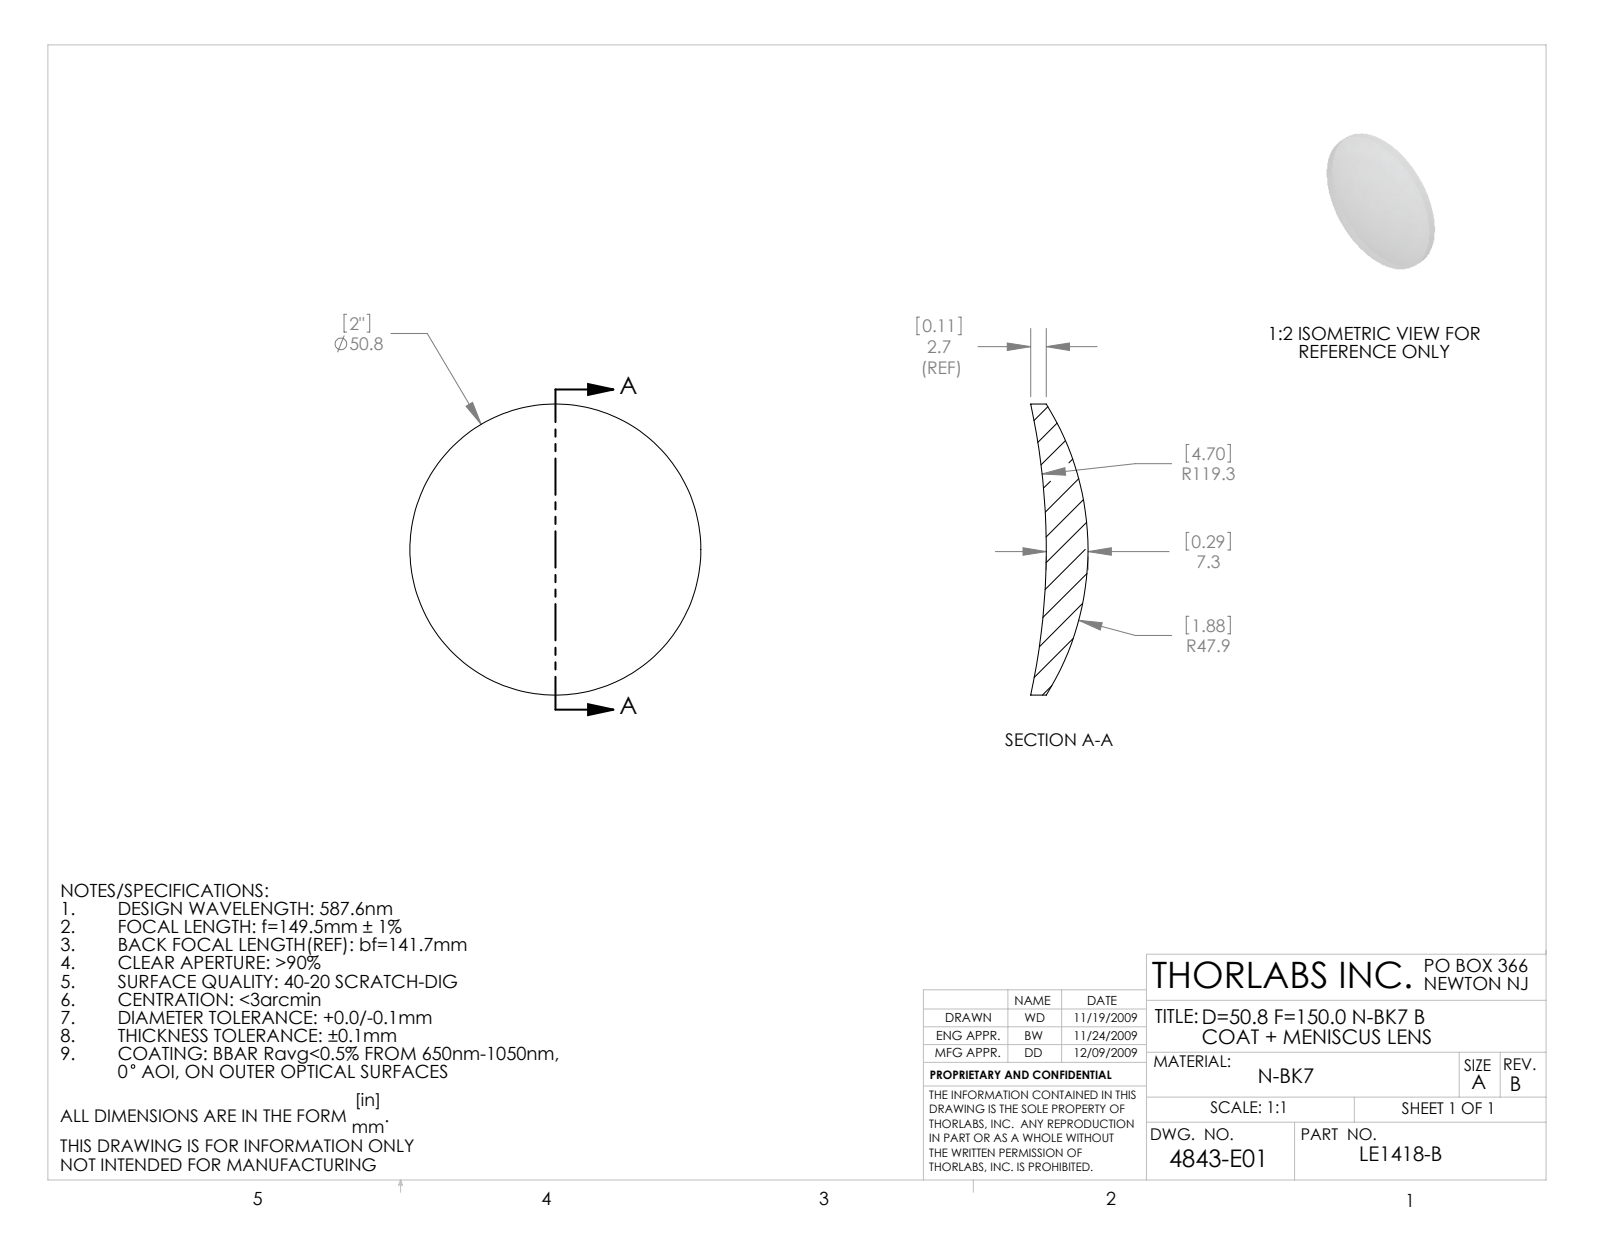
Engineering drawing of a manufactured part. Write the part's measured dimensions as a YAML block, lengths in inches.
part_name: "4843-E0W"
step_written_by: "SolidWorks 2009 (AUTOMOTIVE_DESIGN)"
units: inches
bodies: {solids: 1, faces: 6, planar: 0, cylindrical: 2, other: 4}
overall_size: [2, 2, 0.395]
volume: 0.631
surface_area: 7.254
round_bosses_or_shafts:
  - {diameter: 2, count: 1}
